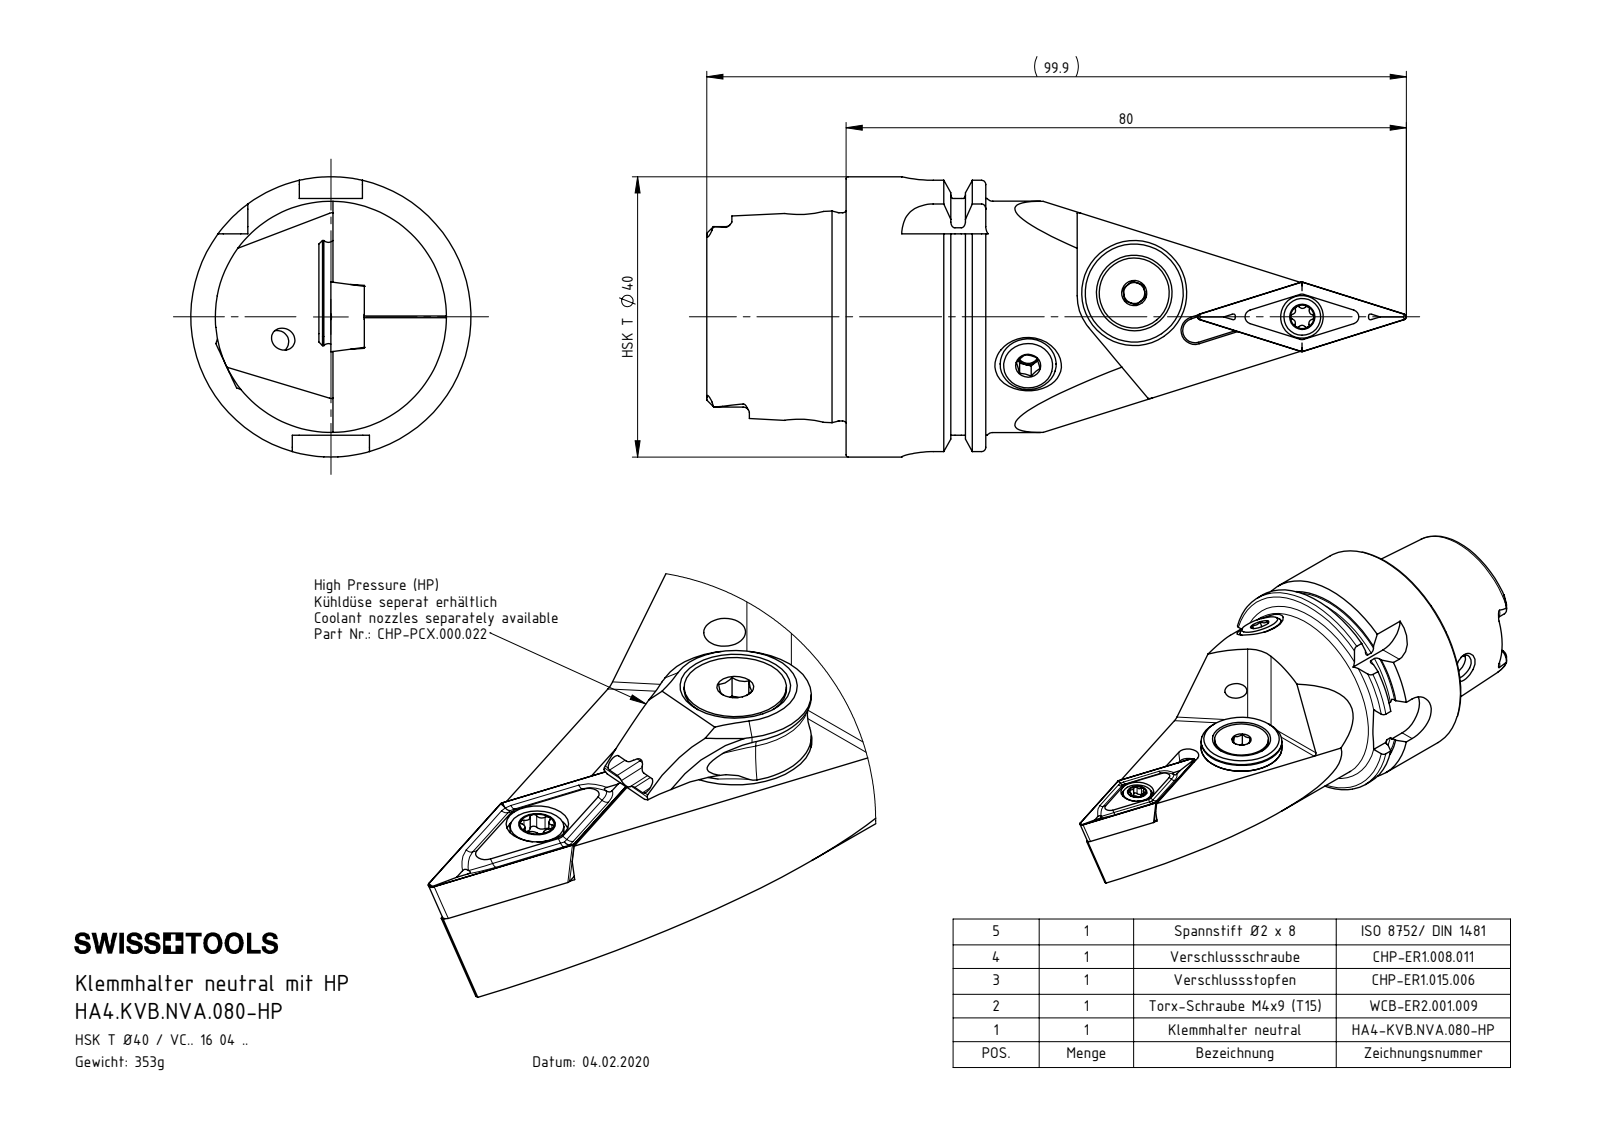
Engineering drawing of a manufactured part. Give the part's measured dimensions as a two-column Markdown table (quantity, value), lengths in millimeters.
| quantity | value |
| --- | --- |
| part name | DIN 3771 - 6.5x1.5; ISO 8752 2x8; DIN 3771 - 13x1; HA4.KVB.NVA.080-HP (+7 more) |
| STEP written by | SolidWorks 2017 (AUTOMOTIVE_DESIGN) |
| units | millimeters |
| bodies | 9 solids, 407 faces (132 planar, 105 cylindrical, 170 other) |
| overall size | 99.9 × 40 × 40 |
| volume | 44 451 mm³ |
| surface area | 17 550 mm² |
| round holes (diameter × count) | 4.2 × 3, 3.3 × 2, 1.2 × 1, 2 × 1, 3 × 1, 4.4 × 1, 4.6 × 1, 5 × 1, 5.3 × 1, 6.1 × 1, 7 × 1, 10 × 1 |
| round bosses / shafts (diameter × count) | 40 × 1, 34.75 × 1, 33 × 1, 29.71 × 1, 14.85 × 1, 13.4 × 1, 10 × 1, 8 × 1 |
| partial cylindrical surfaces (radius × count) | 1 × 7, 0.34 × 6, 0.59 × 6, 0.9 × 6, 0.5 × 4, 1.88 × 4, 4.5 × 4, 6 × 3 |
| main face-to-face distances | 4.46, 7.95, 4.5, 19.95, 12, 32, 24.05, 12.05, 19.9, 27.85 |
| hole center spacings | 4.5, 21.45, 21.55, 24.9, 25, 33.23, 37.25, 57.99 |
